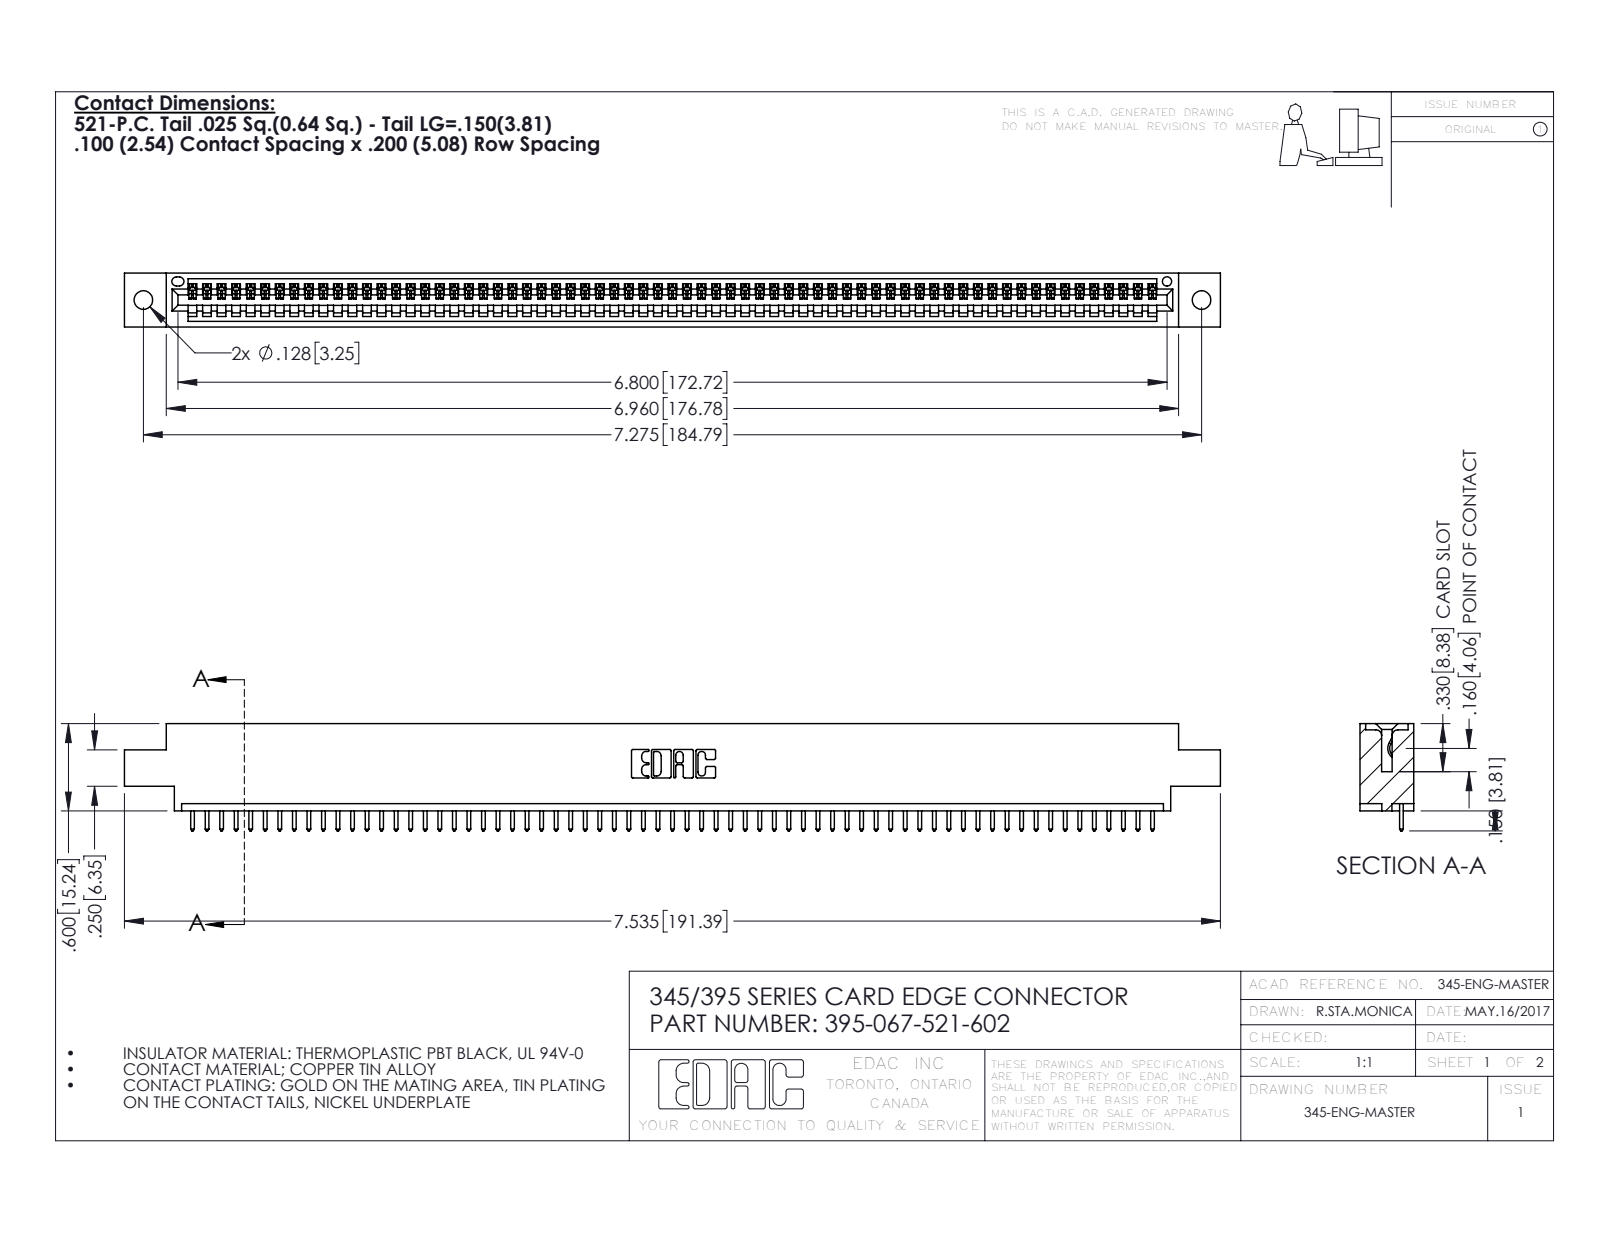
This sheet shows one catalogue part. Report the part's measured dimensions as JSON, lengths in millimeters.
{"part_name": "345-292-001_345-293-121; 395-067-521-602; 345 Part_0.170 Offset - 0.128 Dia", "step_written_by": "SolidWorks 2016 (CONFIG_CONTROL_DESIGN)", "units": "millimeters", "bodies": {"solids": 68, "faces": 4016, "planar": 2764, "cylindrical": 1252, "other": 0}, "overall_size": [191.4, 18.7, 9.4], "volume_mm3": 18040, "surface_area_mm2": 23430, "round_holes": [[3.3, 2], [1.6, 1]], "partial_cylinders_radius": [[0.2, 134], [0.3, 134], [0.3, 22], [0.2, 6], [0.8, 6], [0.7, 3], [0.8, 2], [1, 2]], "face_to_face_distances": [7.6, 1.8, 9.4, 5.1, 2.5, 6.9, 0.6, 5.7, 4.4, 3.8], "hole_center_spacings": [6.9, 178.8, 184.8]}
